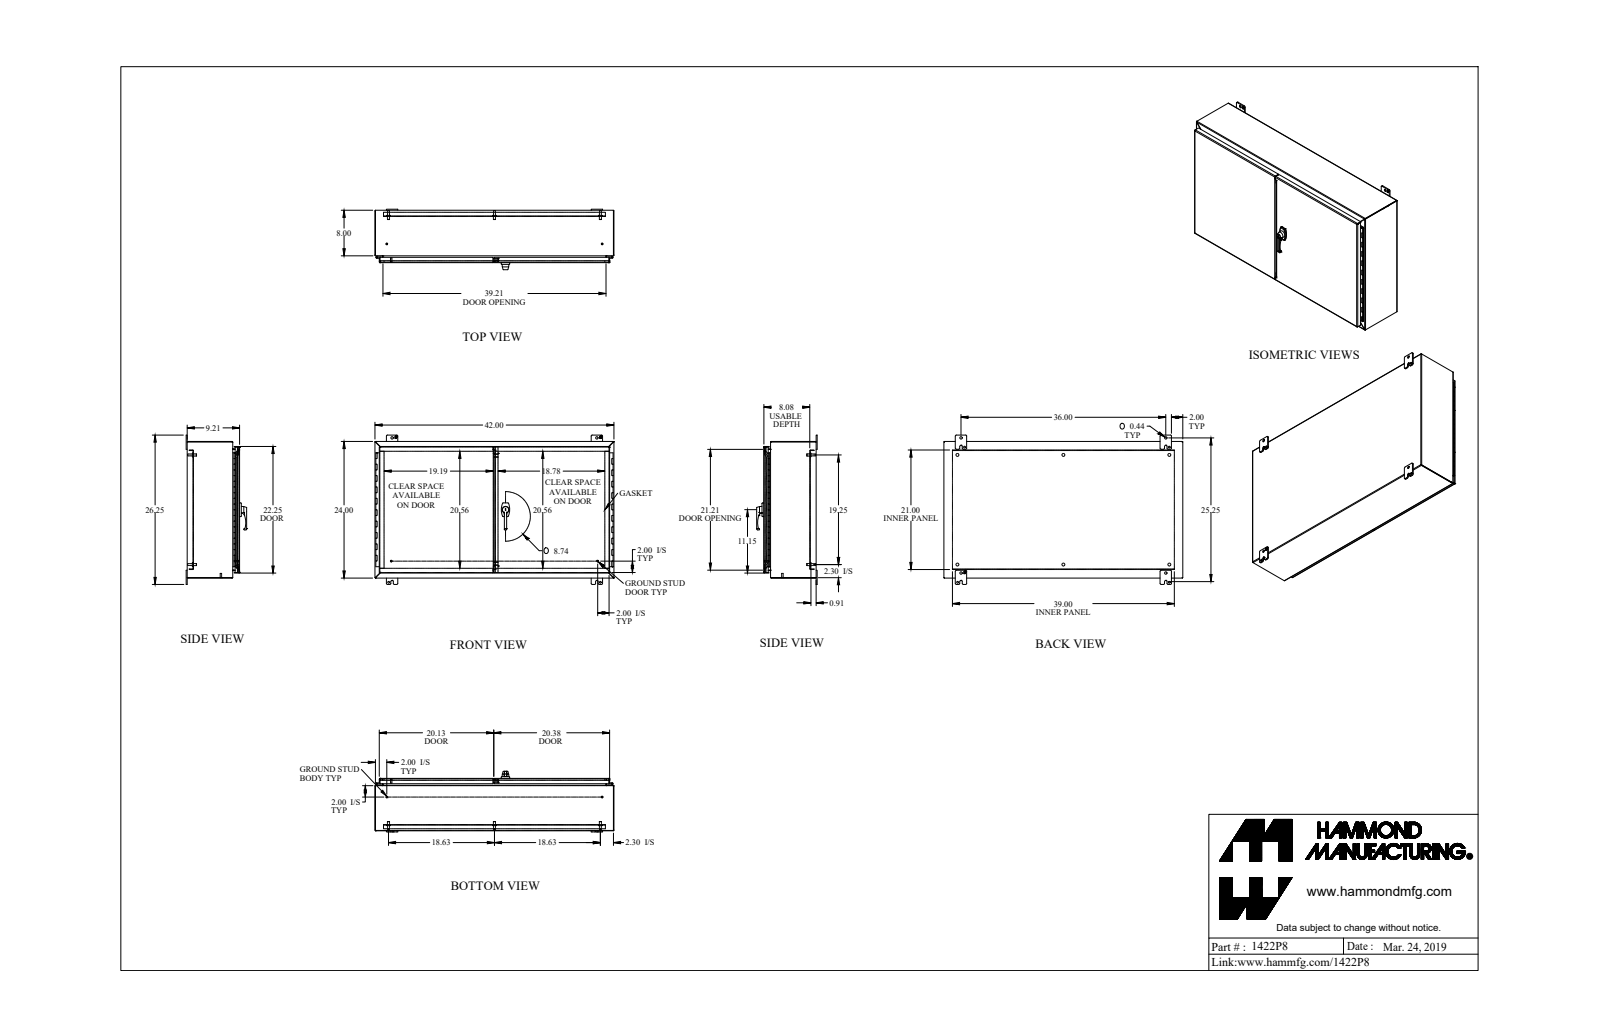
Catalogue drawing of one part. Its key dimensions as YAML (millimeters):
part_name: "1422P8"
step_written_by: "SolidWorks 2019 (AUTOMOTIVE_DESIGN)"
units: millimeters
bodies: {solids: 0, faces: 1493, planar: 920, cylindrical: 423, other: 150}
overall_size: [1066.8, 666.8, 270.2]
round_holes:
  - {diameter: 7.7, count: 8}
  - {diameter: 7.8, count: 7}
  - {diameter: 11.3, count: 6}
  - {diameter: 12.7, count: 6}
  - {diameter: 5.5, count: 4}
  - {diameter: 8, count: 4}
  - {diameter: 11.1, count: 4}
  - {diameter: 5.5, count: 3}
  - {diameter: 2.8, count: 2}
  - {diameter: 3.2, count: 2}
  - {diameter: 4, count: 2}
  - {diameter: 4.7, count: 2}
round_bosses_or_shafts:
  - {diameter: 25.4, count: 7}
  - {diameter: 16.5, count: 6}
  - {diameter: 9.5, count: 6}
  - {diameter: 8.4, count: 6}
  - {diameter: 12.7, count: 5}
  - {diameter: 8, count: 4}
  - {diameter: 7.1, count: 4}
  - {diameter: 6.4, count: 4}
partial_cylinders:
  - {radius: 4.8, count: 27}
  - {radius: 1.2, count: 18}
  - {radius: 3.6, count: 18}
  - {radius: 0.9, count: 16}
  - {radius: 1.3, count: 16}
  - {radius: 2.7, count: 16}
  - {radius: 2.5, count: 9}
  - {radius: 1.1, count: 8}
face_to_face_distances: [1.8, 229.7, 231.5, 2.4, 2.4, 23.8, 232.1, 233.9, 205.9, 203.5]
hole_center_spacings: [473.1, 680.3, 152.4, 513.2, 1037.2, 43, 172.9, 323.1]
